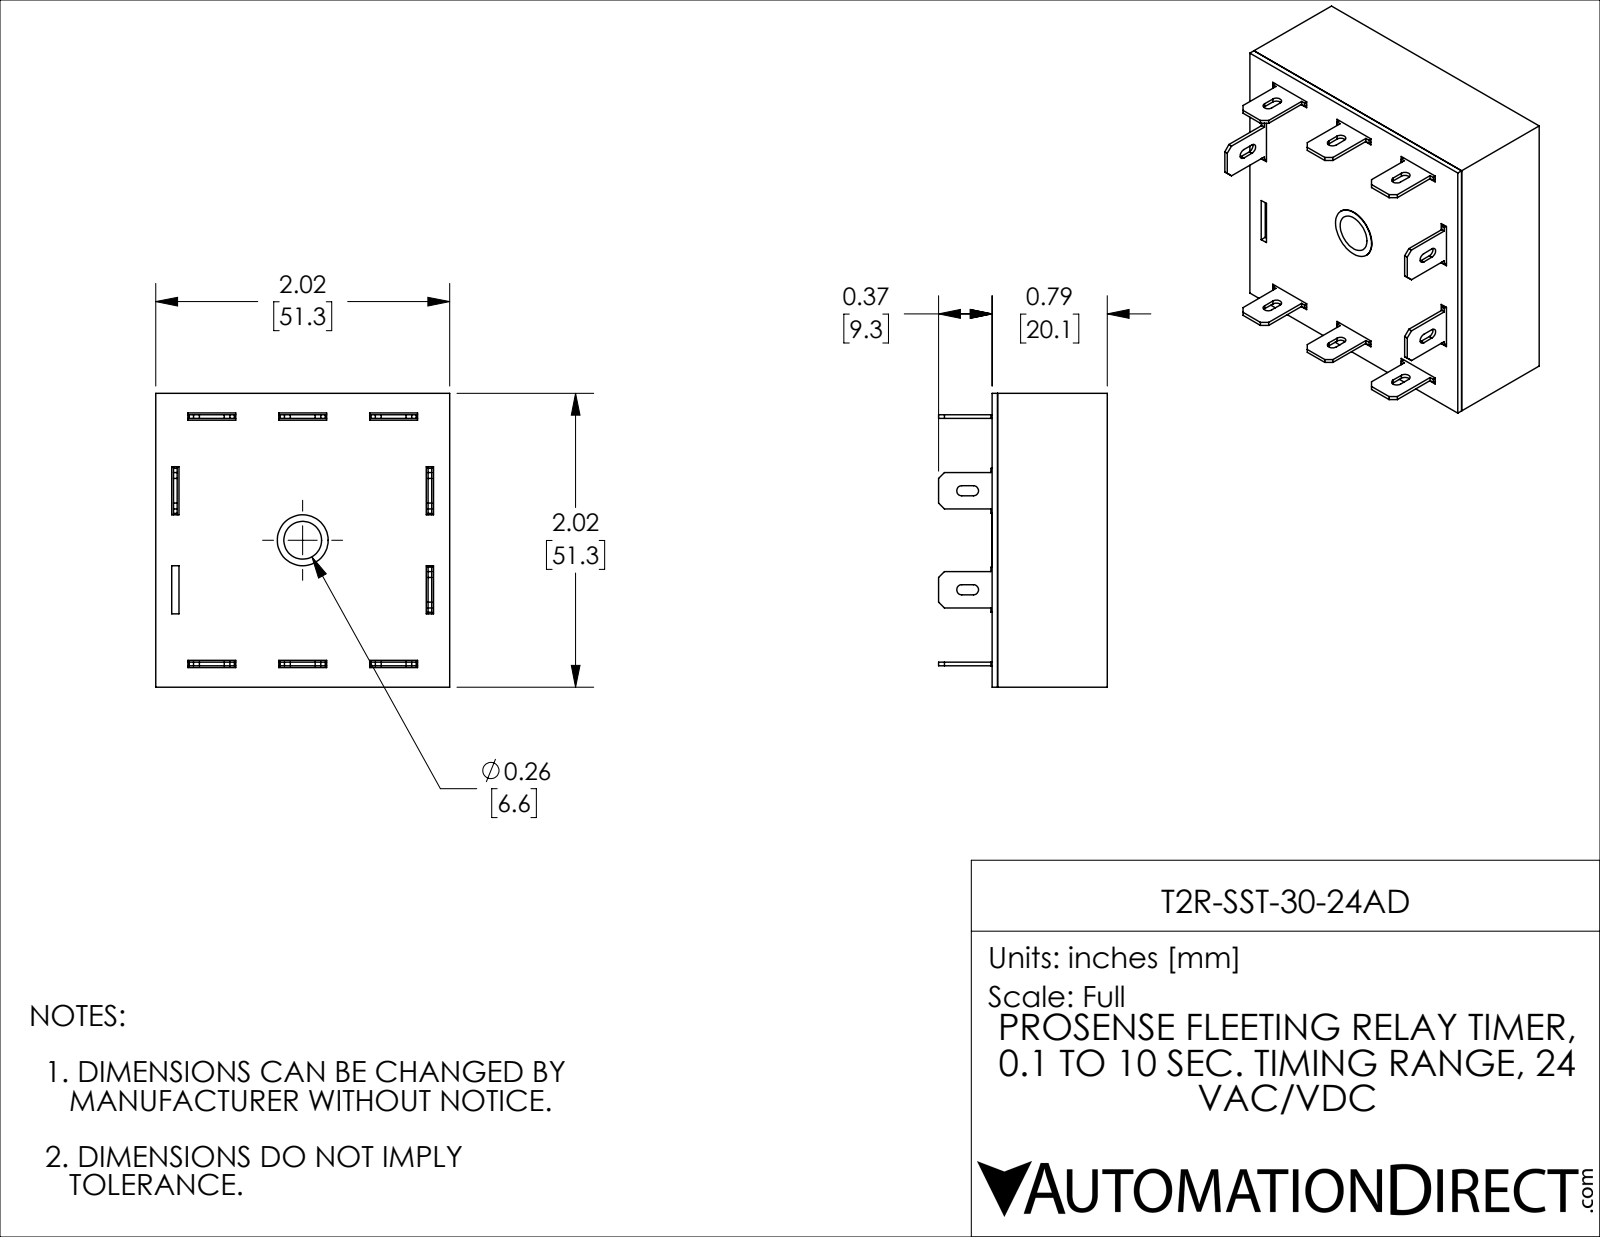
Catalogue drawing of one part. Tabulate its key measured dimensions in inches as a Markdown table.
| quantity | value |
| --- | --- |
| part name | T2R-SST-30-24AD |
| STEP written by | SolidWorks 2021 (CONFIG_CONTROL_DESIGN) |
| units | inches |
| bodies | 11 solids, 280 faces (256 planar, 22 cylindrical, 2 other) |
| overall size | 2.02 × 2.02 × 1.16 |
| volume | 0.682 in³ |
| surface area | 36.12 in² |
| round holes (diameter × count) | 0.35 × 1 |
| partial cylindrical surfaces (radius × count) | 0.035 × 10 |
| main face-to-face distances | 0.045, 1.975, 0.754, 0.792, 0.038, 0.709, 0.747, 2.02, 0.147, 1.872 |
